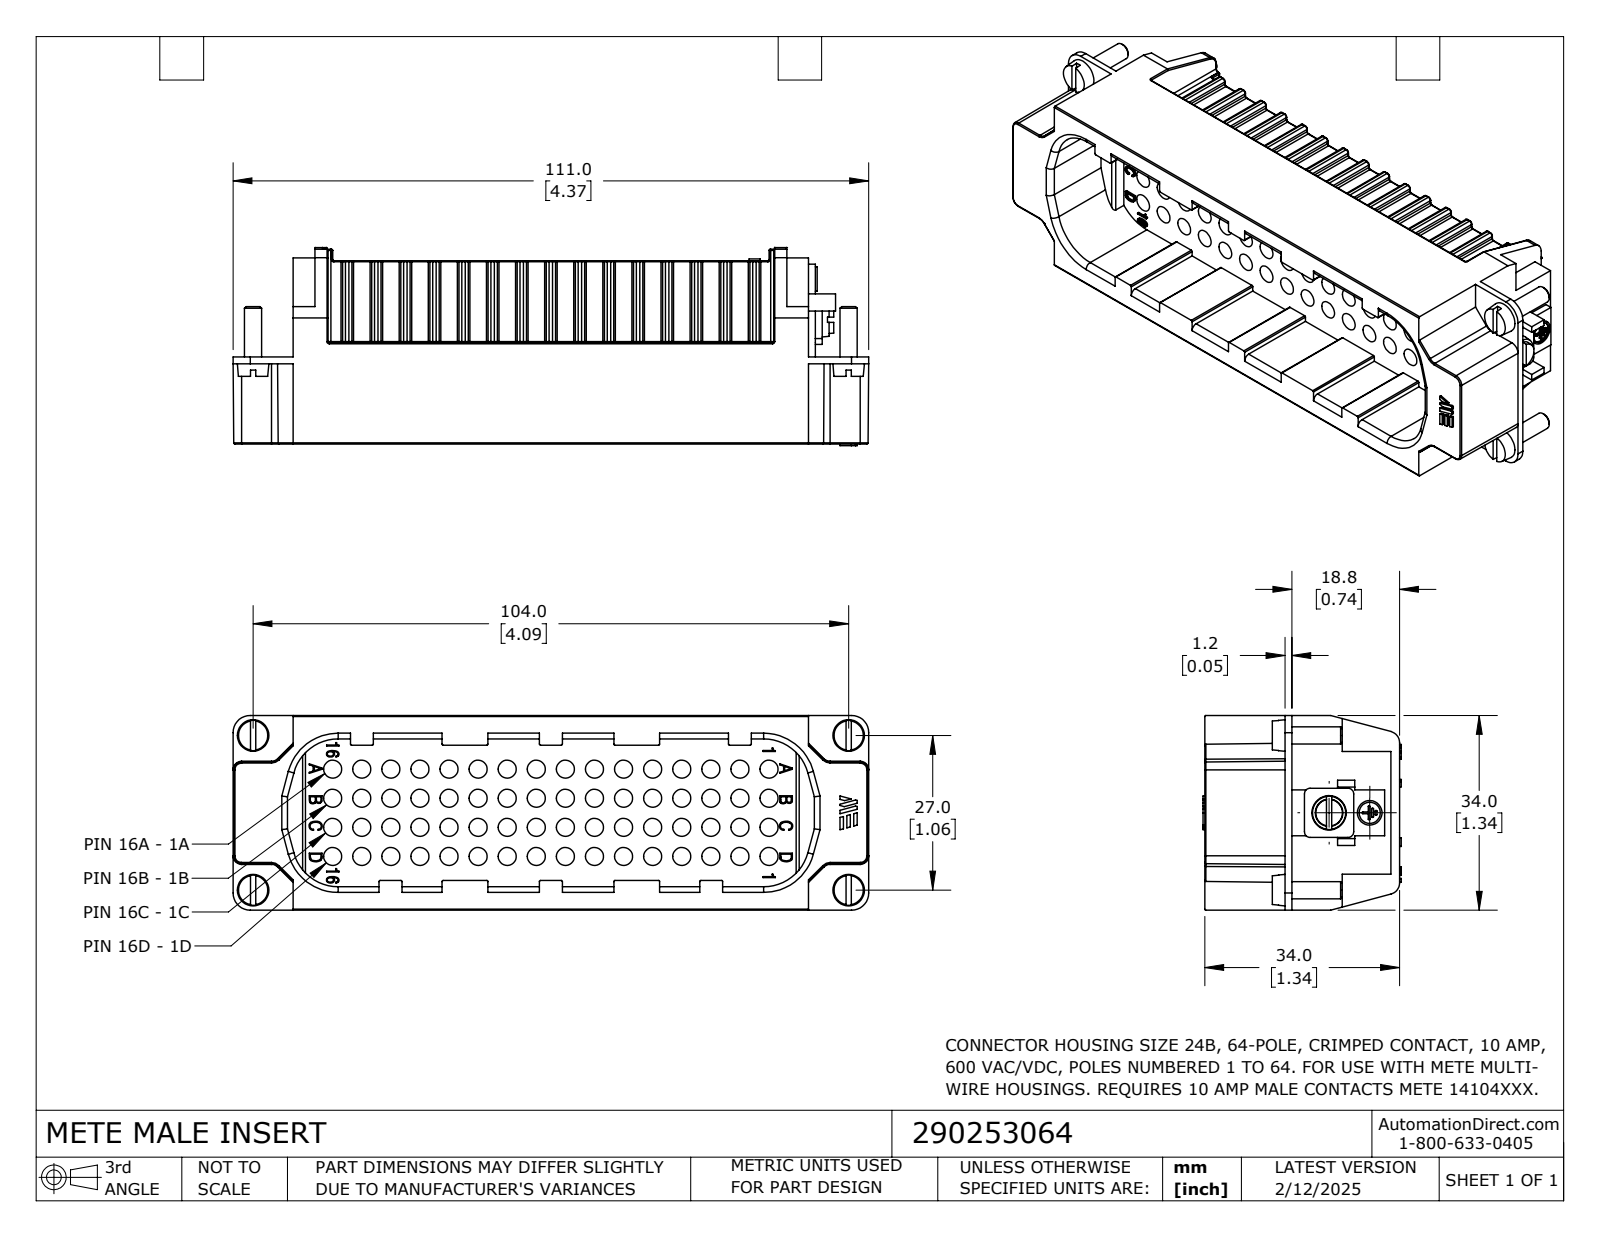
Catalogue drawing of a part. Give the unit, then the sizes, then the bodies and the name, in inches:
Units: inches
Overall size (bounding box): 4.37 × 1.362 × 1.339
Round holes (diameter × count): ⌀0.124 ×64, ⌀0.146 ×1
Round bosses / shafts (diameter × count): ⌀0.118 ×4, ⌀0.169 ×1
Partial cylindrical surfaces — rounded edges, fillets, slot ends (radius × count): R0.008 ×122, R0.02 ×66, R0.012 ×60, R0.004 ×14, R0.039 ×12, R0.085 ×8, R0.118 ×4, R0.315 ×4
Main face-to-face distances: 1.339, 0.929, 0.043, 0.248, 0.087, 1.091, 0.161, 1.177, 0.669, 0.591
Hole centre spacings: 0.447, 0.632, 0.2, 0.283, 0.4, 1.02, 1.414, 0.825
Volume: 3.022 in³ · Surface area: 48.41 in²
Bodies: 1 solid, 1571 faces (485 planar, 648 cylindrical, 438 other)
Part name (STEP PRODUCT): 290253064
STEP written by: SolidWorks 2024 (CONFIG_CONTROL_DESIGN)
